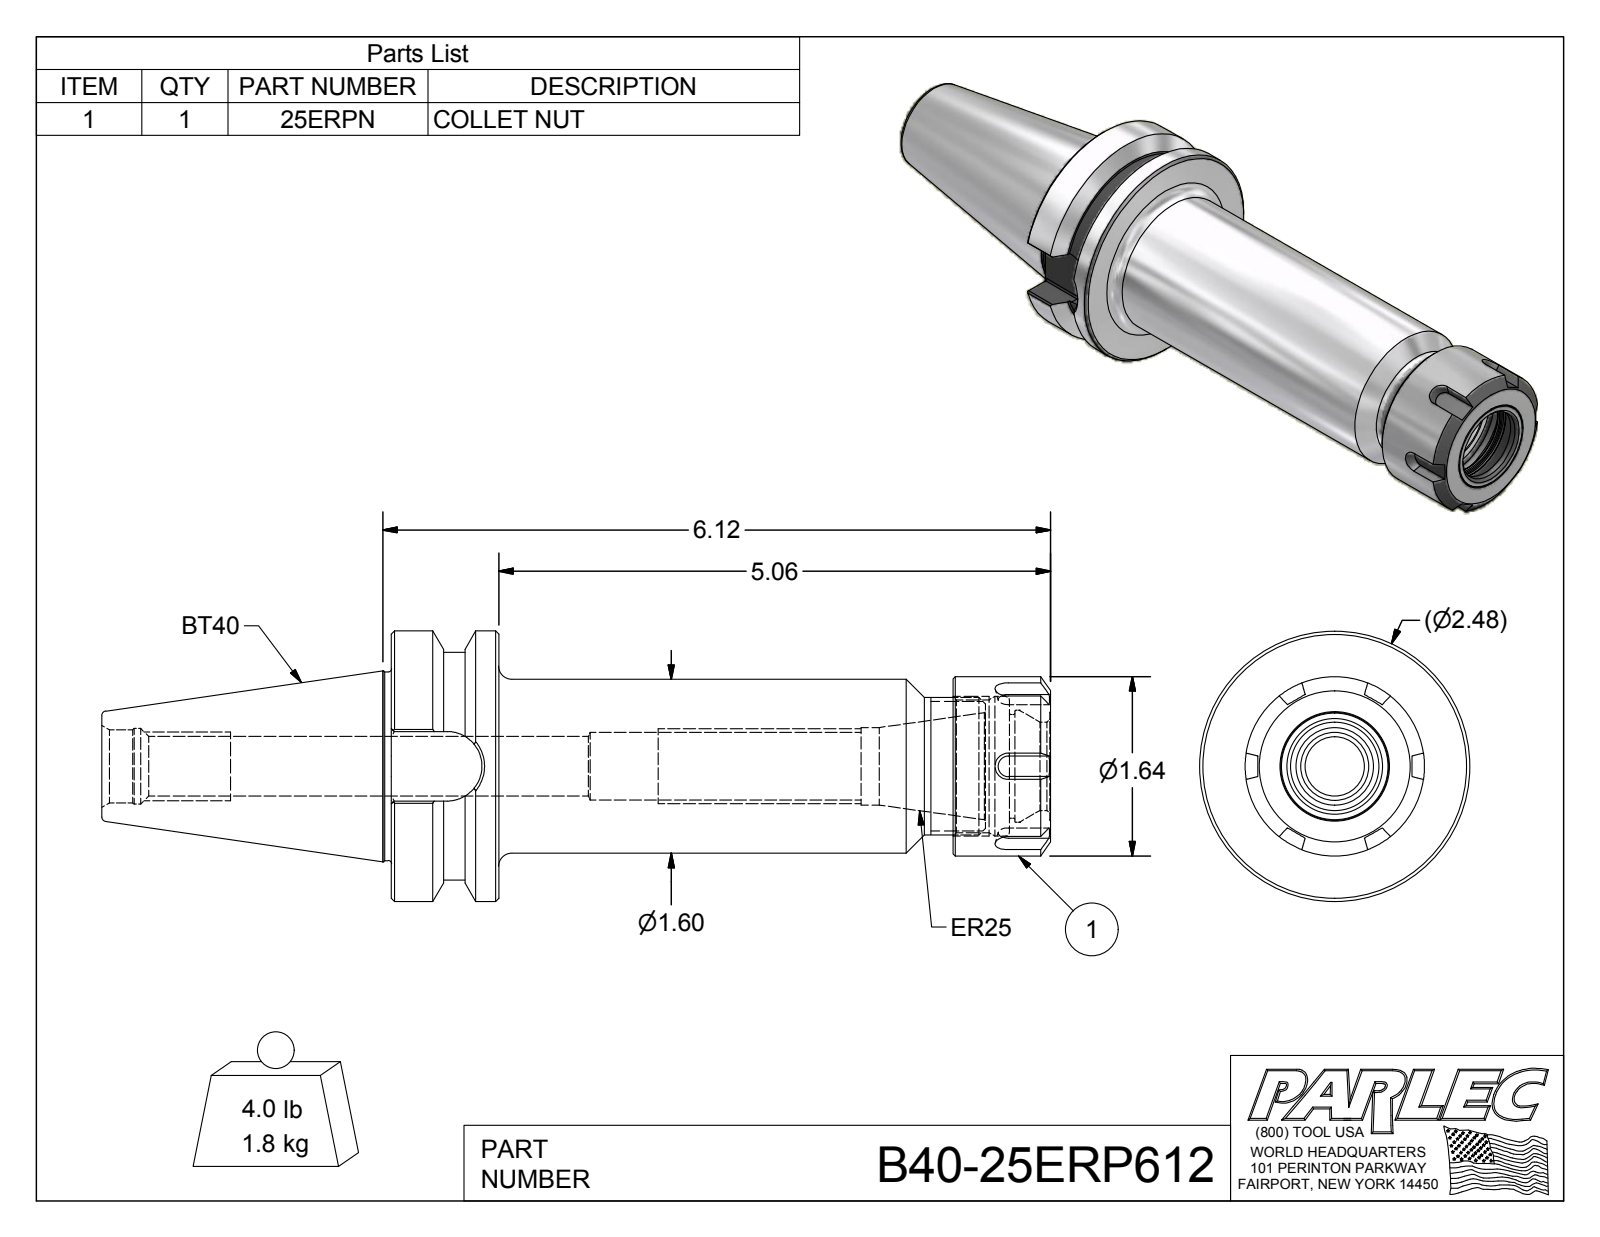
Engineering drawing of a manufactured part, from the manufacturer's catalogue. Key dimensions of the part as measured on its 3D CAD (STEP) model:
Part name (STEP PRODUCT): B40-25ERP612; B40-25ER6-1; 25ERPN
STEP written by: Autodesk Inventor 2012 (AUTOMOTIVE_DESIGN)
Units: inches
Bodies: 2 solids, 119 faces (47 planar, 29 cylindrical, 43 other)
Overall size (bounding box): 8.695 × 2.48 × 2.48
Volume: 15.09 in³ · Surface area: 75.17 in²
Round holes (diameter × count): ⌀0.545 ×1, ⌀0.62 ×1, ⌀0.67 ×1, ⌀0.694 ×1, ⌀0.71 ×1, ⌀0.811 ×1, ⌀0.95 ×1, ⌀1.027 ×1, ⌀1.217 ×1, ⌀1.28 ×1
Round bosses / shafts (diameter × count): ⌀2.48 ×1, ⌀2.087 ×1, ⌀1.73 ×1, ⌀1.643 ×1, ⌀1.595 ×1, ⌀1.26 ×1
Partial cylindrical surfaces — rounded edges, fillets, slot ends (radius × count): R0.02 ×8, R0.319 ×1
Main face-to-face distances: 0.984, 6.042, 5.058, 5.149, 4.165, 0.893, 1.78, 5.667, 4.683, 0.518
